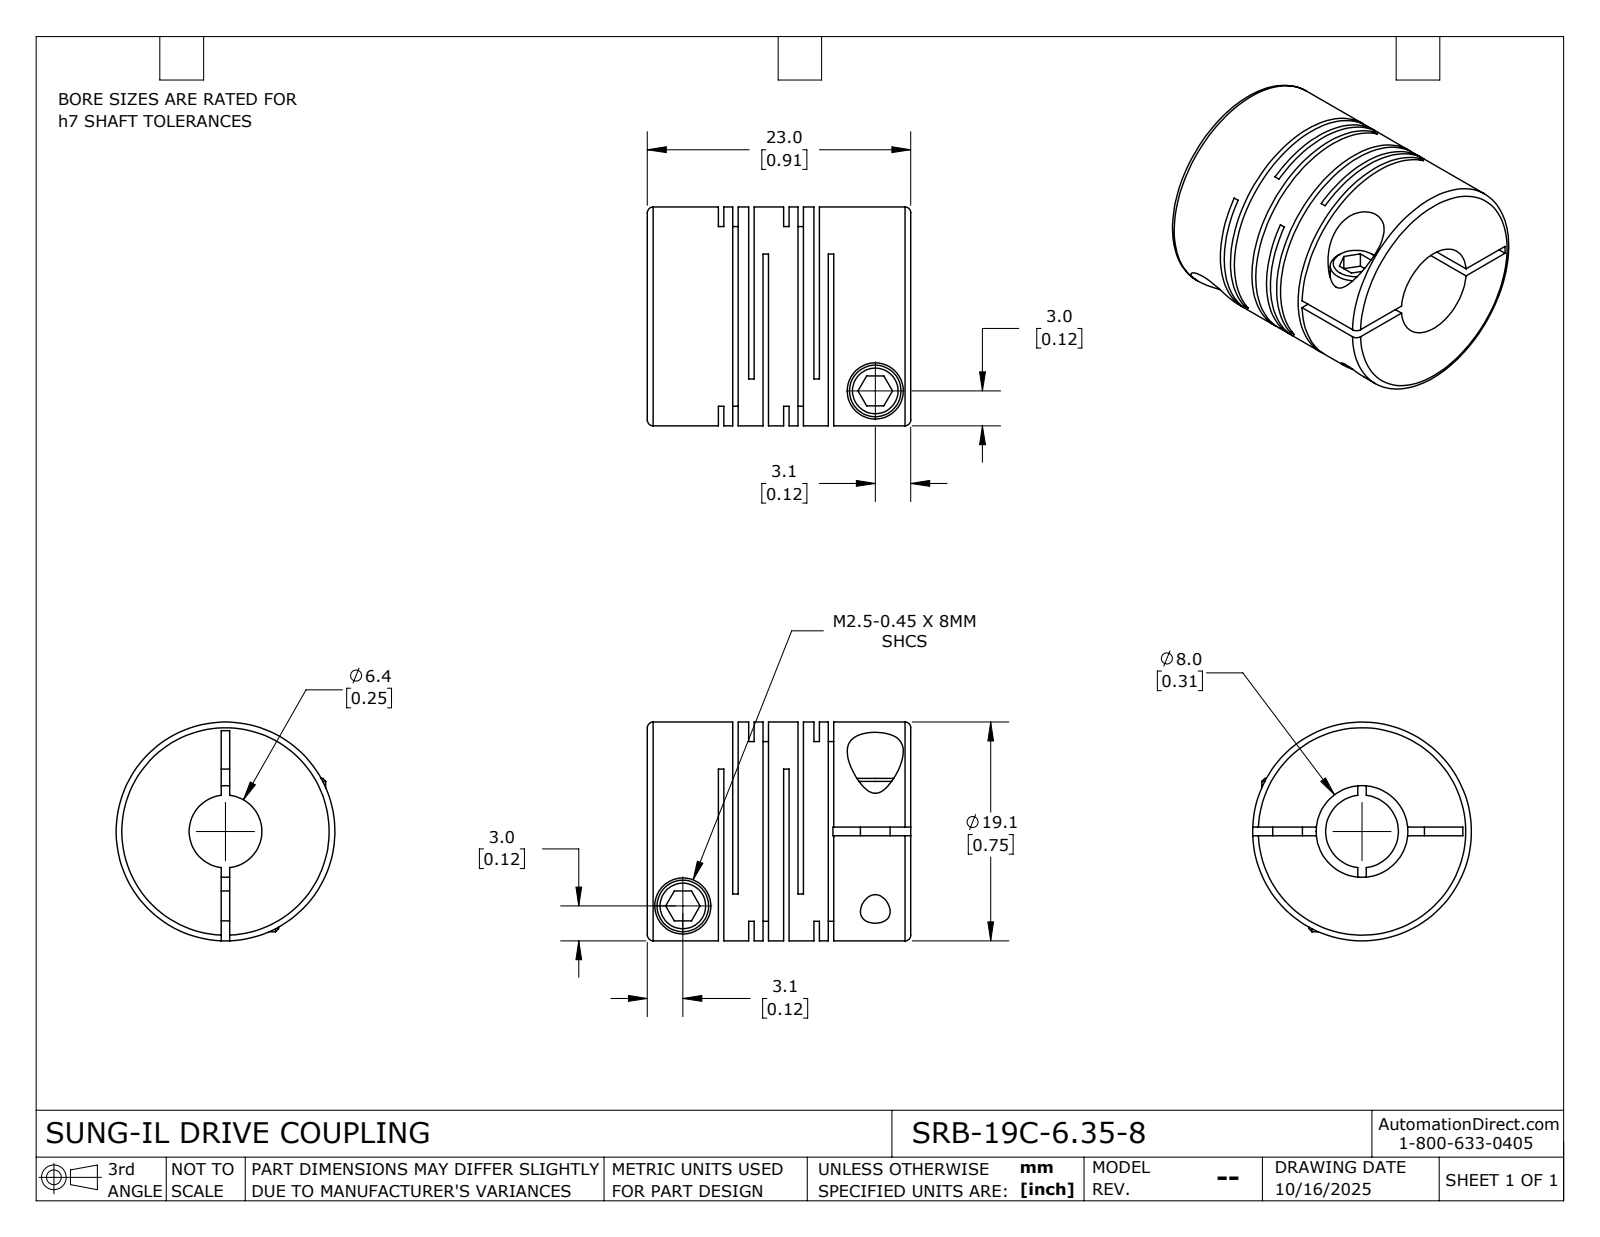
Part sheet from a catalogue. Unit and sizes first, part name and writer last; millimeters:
Units: millimetres
Overall size (bounding box): 23 × 19.1 × 19.1
Round holes (diameter × count): ⌀2.6 ×2, ⌀4.9 ×2, ⌀6.35 ×1, ⌀8 ×1
Round bosses / shafts (diameter × count): ⌀4.5 ×2, ⌀19.1 ×1
Main face-to-face distances: 2.65, 0.48, 5.7, 1.25, 2.17, 3.05, 5.22, 0.77, 4.45, 1.4
Volume: 4 584 mm³ · Surface area: 5 716 mm²
Bodies: 1 solid, 115 faces (60 planar, 42 cylindrical, 13 other)
Part name (STEP PRODUCT): SRB-19C-6.35-8
STEP written by: SolidWorks 2024 (CONFIG_CONTROL_DESIGN)
